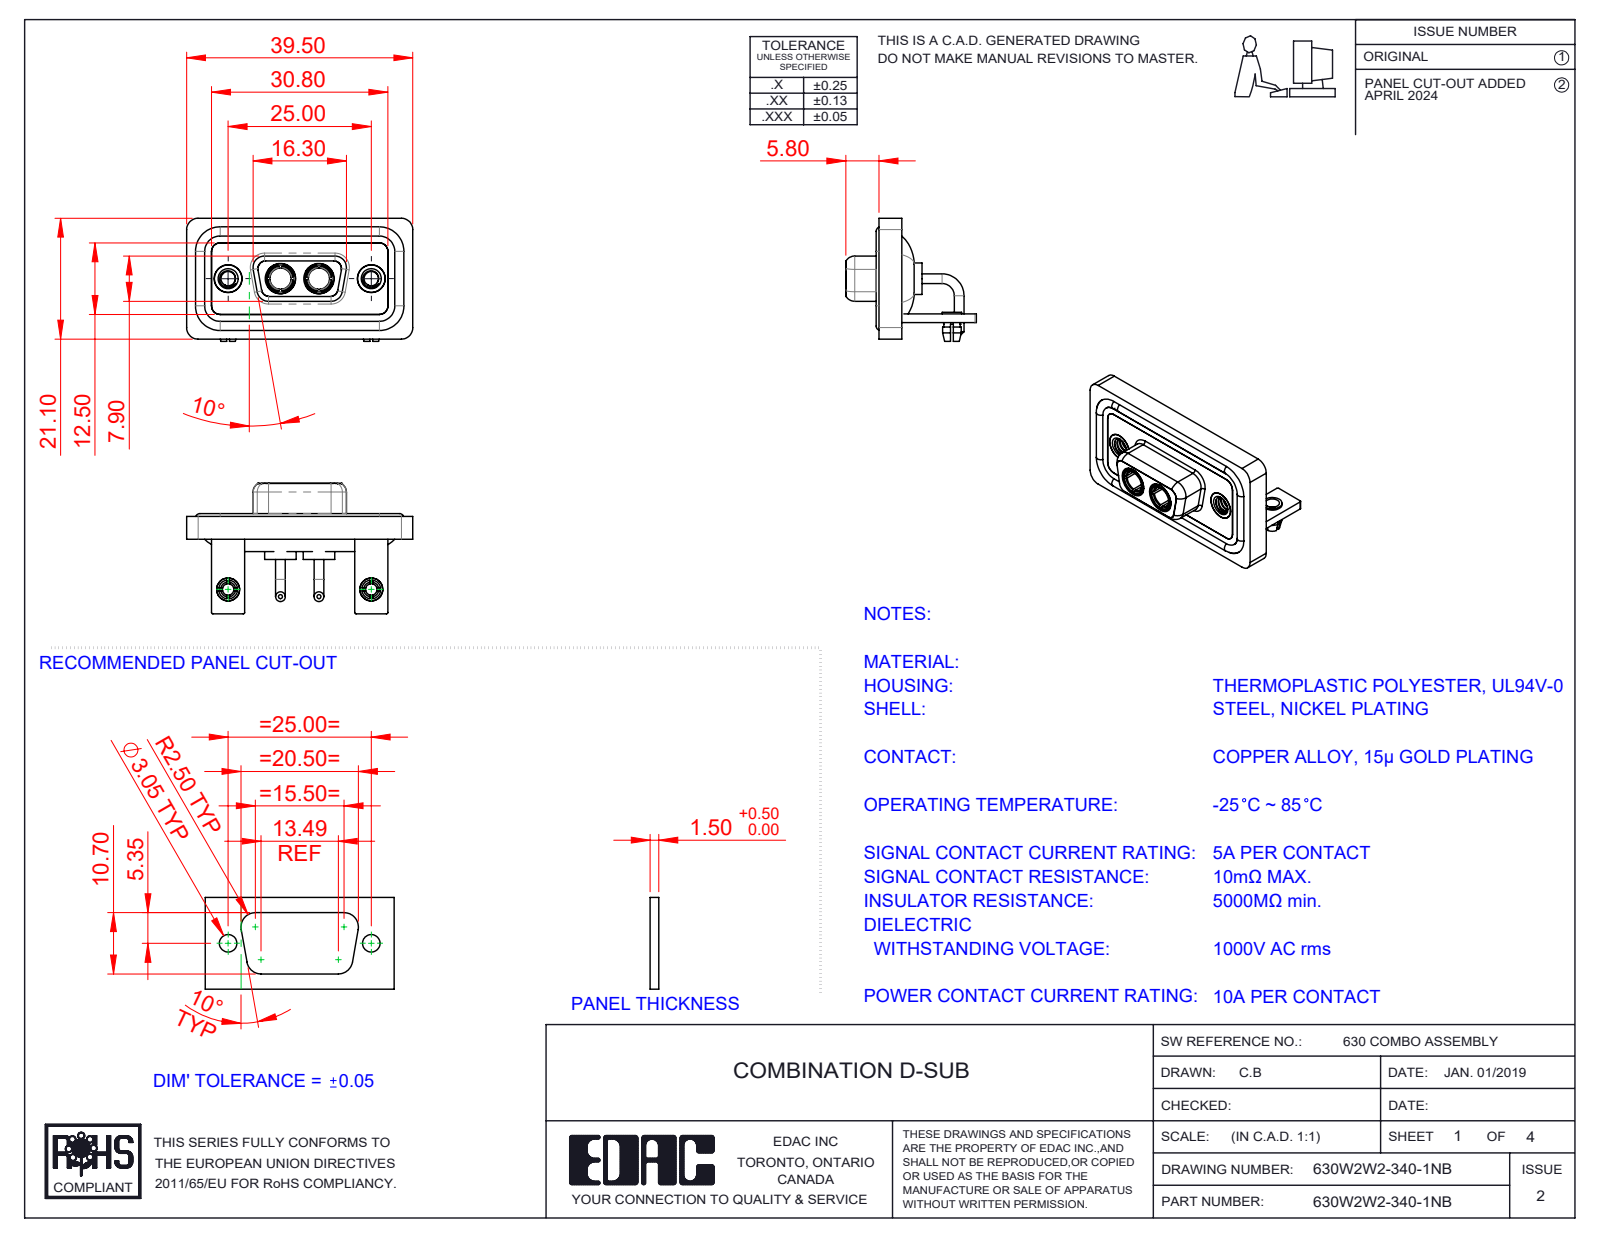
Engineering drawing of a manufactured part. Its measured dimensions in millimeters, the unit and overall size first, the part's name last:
Units: millimetres
Overall size (bounding box): 39.5 × 22.8 × 21.5
Round holes (diameter × count): ⌀2.5 ×4, ⌀4.85 ×4, ⌀2 ×2, ⌀3.2 ×2, ⌀3.7 ×2, ⌀4 ×2, ⌀4.05 ×2, ⌀5 ×2, ⌀5.3 ×2
Round bosses / shafts (diameter × count): ⌀1.7 ×4, ⌀1.6 ×4, ⌀5.5 ×2, ⌀5.2 ×2, ⌀4.96 ×2, ⌀4.95 ×2, ⌀4.8 ×2, ⌀4.75 ×2
Partial cylindrical surfaces — rounded edges, fillets, slot ends (radius × count): R2 ×19, R1.5 ×18, R0.25 ×16, R1.35 ×8, R1.6 ×8, R0.5 ×5, R0.6 ×4, R0.65 ×4
Main face-to-face distances: 0.4, 2.9, 1.5, 1.8, 1.1, 3.7, 0.8, 2.5, 1.6, 3.1
Hole centre spacings: 9.14, 15.86, 25, 6.72
Volume: 5 096 mm³ · Surface area: 8 633 mm²
Bodies: 15 solids, 676 faces (231 planar, 292 cylindrical, 153 other)
Part name (STEP PRODUCT): 630Combo Board Lock_50 Contacts; 630Combo Shell Front_09 Contacts; 630Combo Stabilizer Bracket_50 Contacts; 630Combo Threaded Rivet_A (+5 more)
STEP written by: SolidWorks 2023 (CONFIG_CONTROL_DESIGN)
